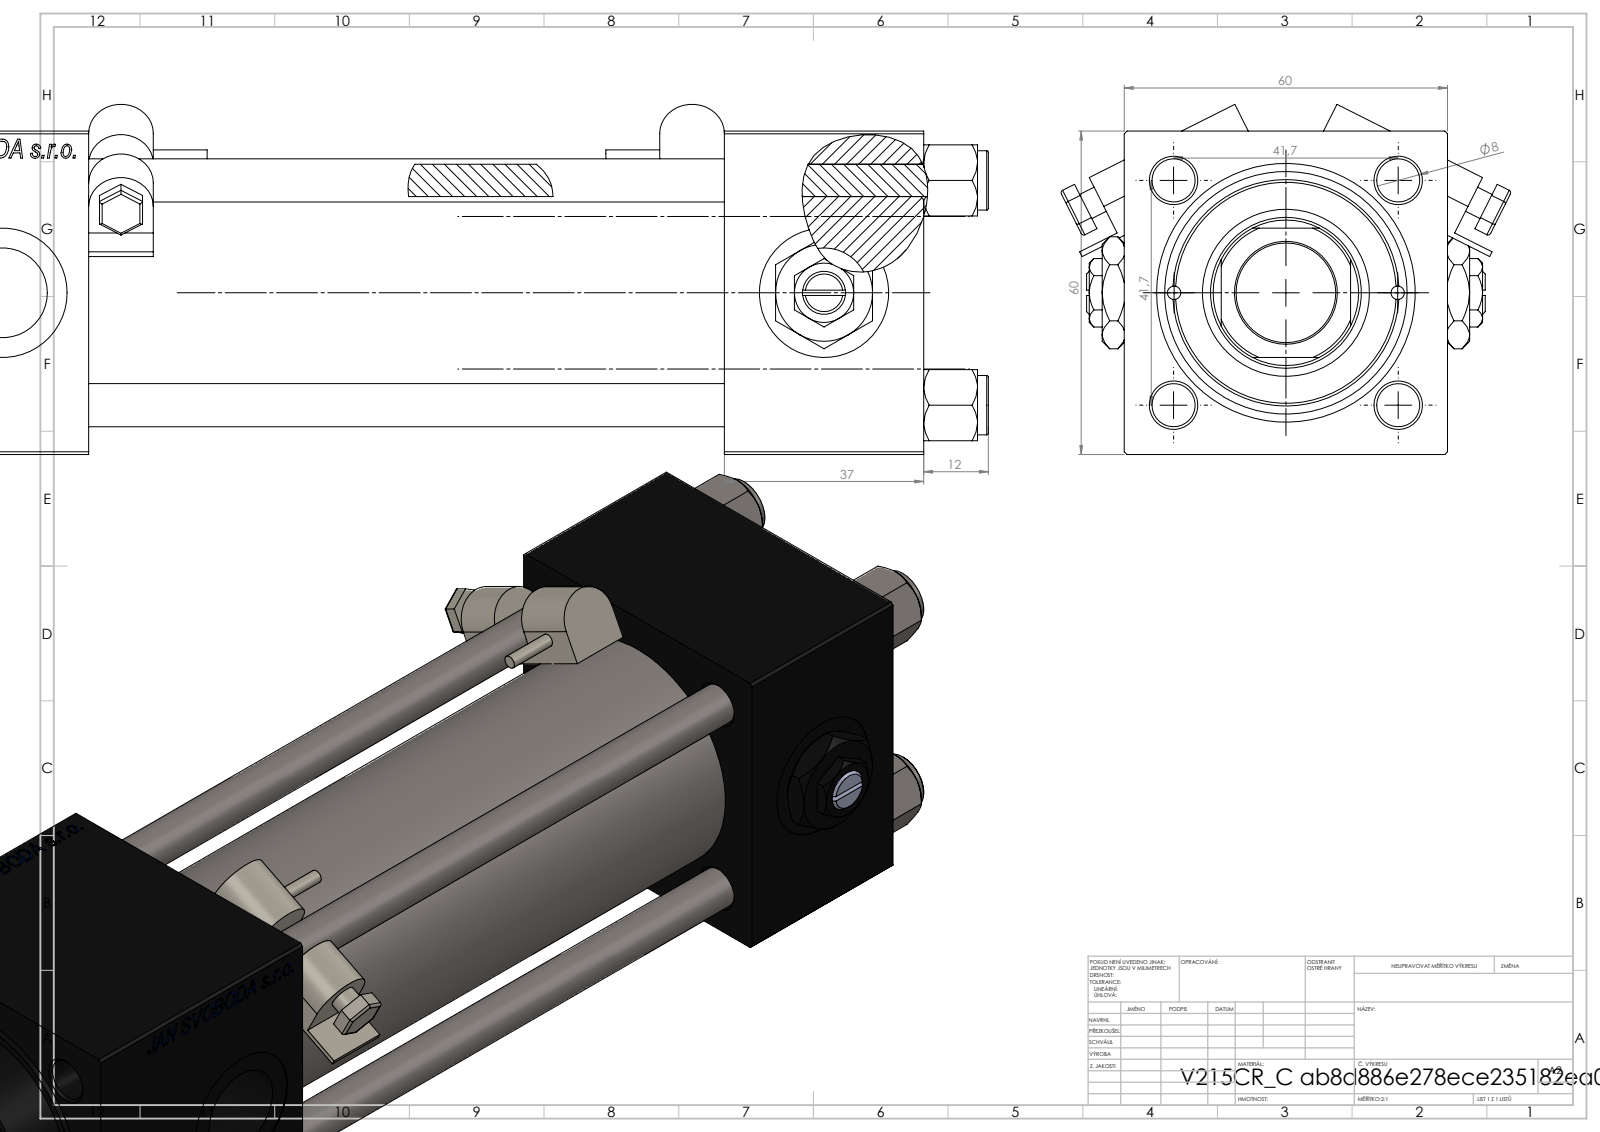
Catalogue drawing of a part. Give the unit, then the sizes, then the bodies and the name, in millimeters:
Units: millimetres
Overall size (bounding box): 245 × 83.44 × 64.97
Round holes (diameter × count): ⌀8 ×4, ⌀2.5 ×2, ⌀7 ×2, ⌀16.66 ×2, ⌀24 ×2, ⌀18.5 ×1, ⌀28 ×1, ⌀31 ×1, ⌀40 ×1, ⌀45 ×1
Round bosses / shafts (diameter × count): ⌀11 ×4, ⌀5 ×2, ⌀2.5 ×2, ⌀46 ×1, ⌀42 ×1
Partial cylindrical surfaces — rounded edges, fillets, slot ends (radius × count): R0.5 ×12, R6 ×4, R13.5 ×1
Main face-to-face distances: 60, 37, 155, 118, 171, 179.3, 142.3, 24.3, 53, 208
Hole centre spacings: 20.85, 29.49, 41.7, 46.53, 20.75, 58.97, 41.5, 152.5
Volume: 501 214 mm³ · Surface area: 146 289 mm²
Bodies: 15 solids, 1320 faces (612 planar, 130 cylindrical, 578 other)
Part name (STEP PRODUCT): V215CR_VCP_C; V215_VC_A; MSRF_MSRG1; V215CR_C_TYCINKA (+3 more)
STEP written by: SolidWorks 2019 (CONFIG_CONTROL_DESIGN)
